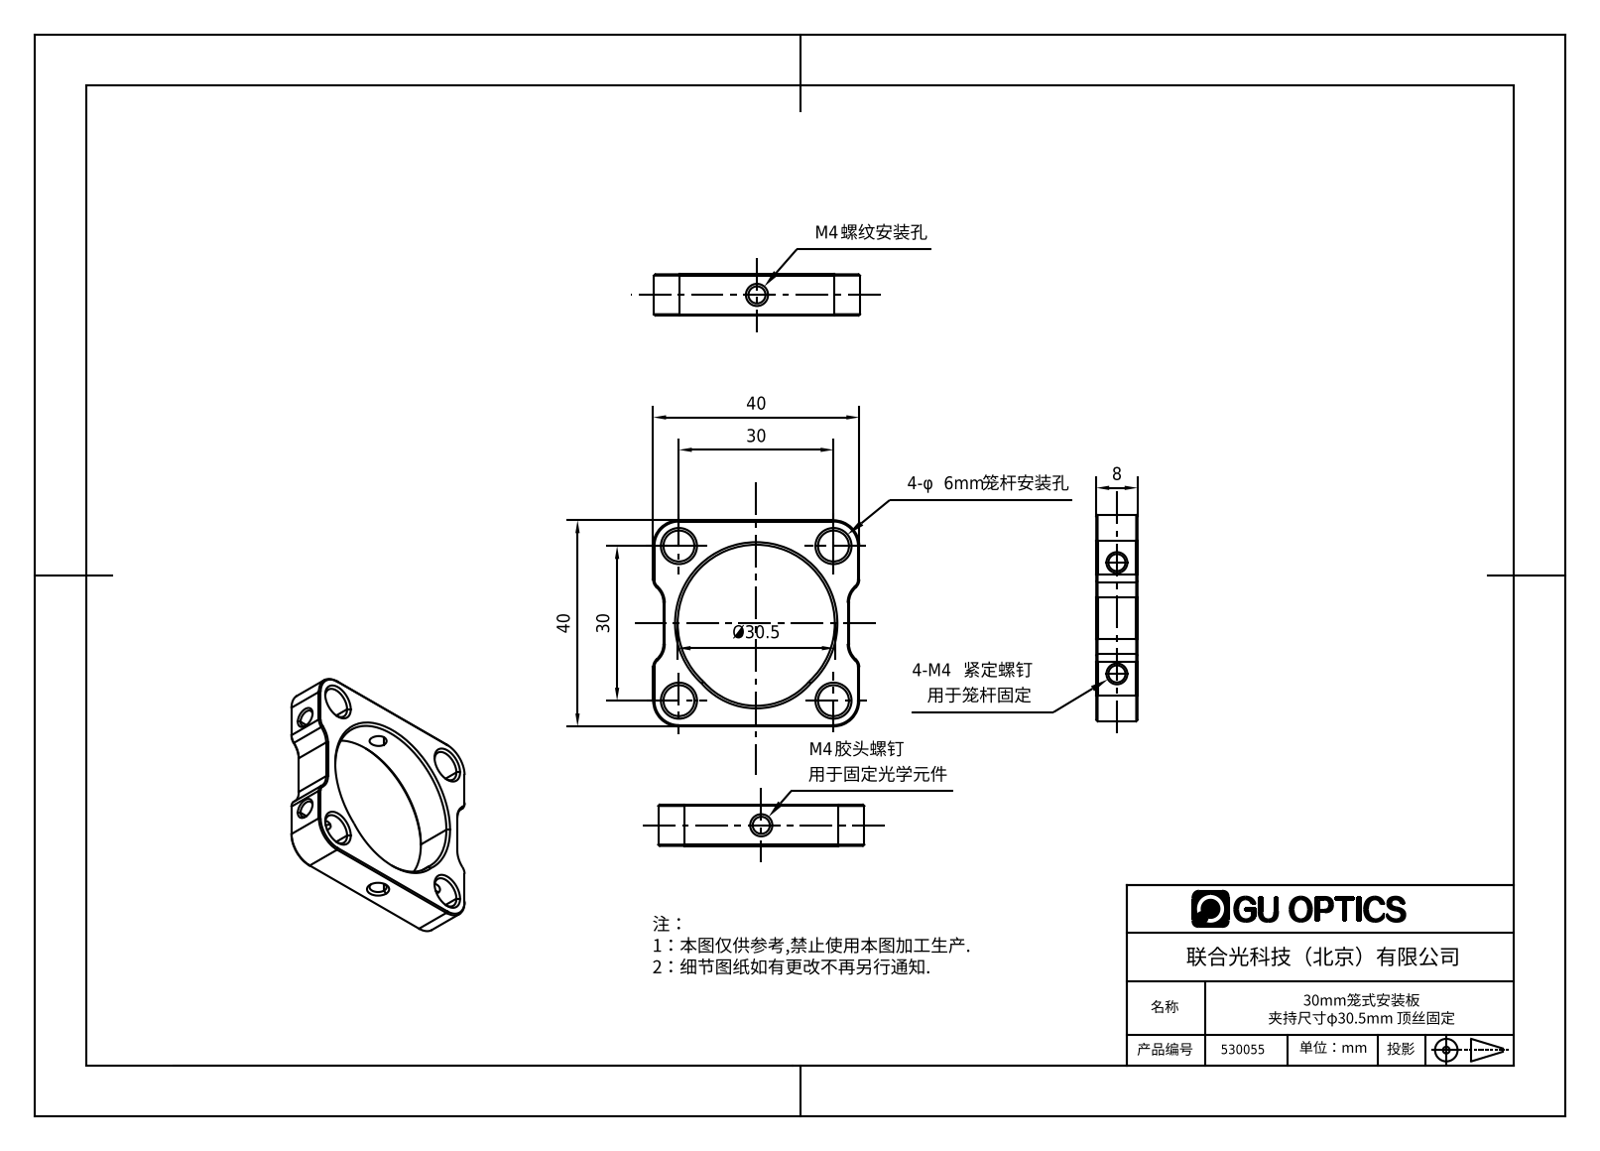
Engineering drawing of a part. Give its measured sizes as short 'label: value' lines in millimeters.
name: 2.2.1.14_L30B-T1.2_30 mm笼板，用于1.2英寸通孔，侧边顶丝固定，M4螺纹
written by: SolidWorks 2018 (AUTOMOTIVE_DESIGN)
unit: mm
bodies: 0 solids, 217 faces (67 planar, 38 cylindrical, 112 other)
size: 40 × 40 × 8
holes: 4× ⌀6, 3× ⌀3.3
bosses: 1× ⌀3
rounds: 4× R2, 4× R4, 4× R5, 1× R13.5, 1× R15.25
face distances: 8, 40, 2, 38, 36, 33.58, 2.1, 32.17, 1.41, 17.15
hole spacings: 30, 42.43, 21.6
